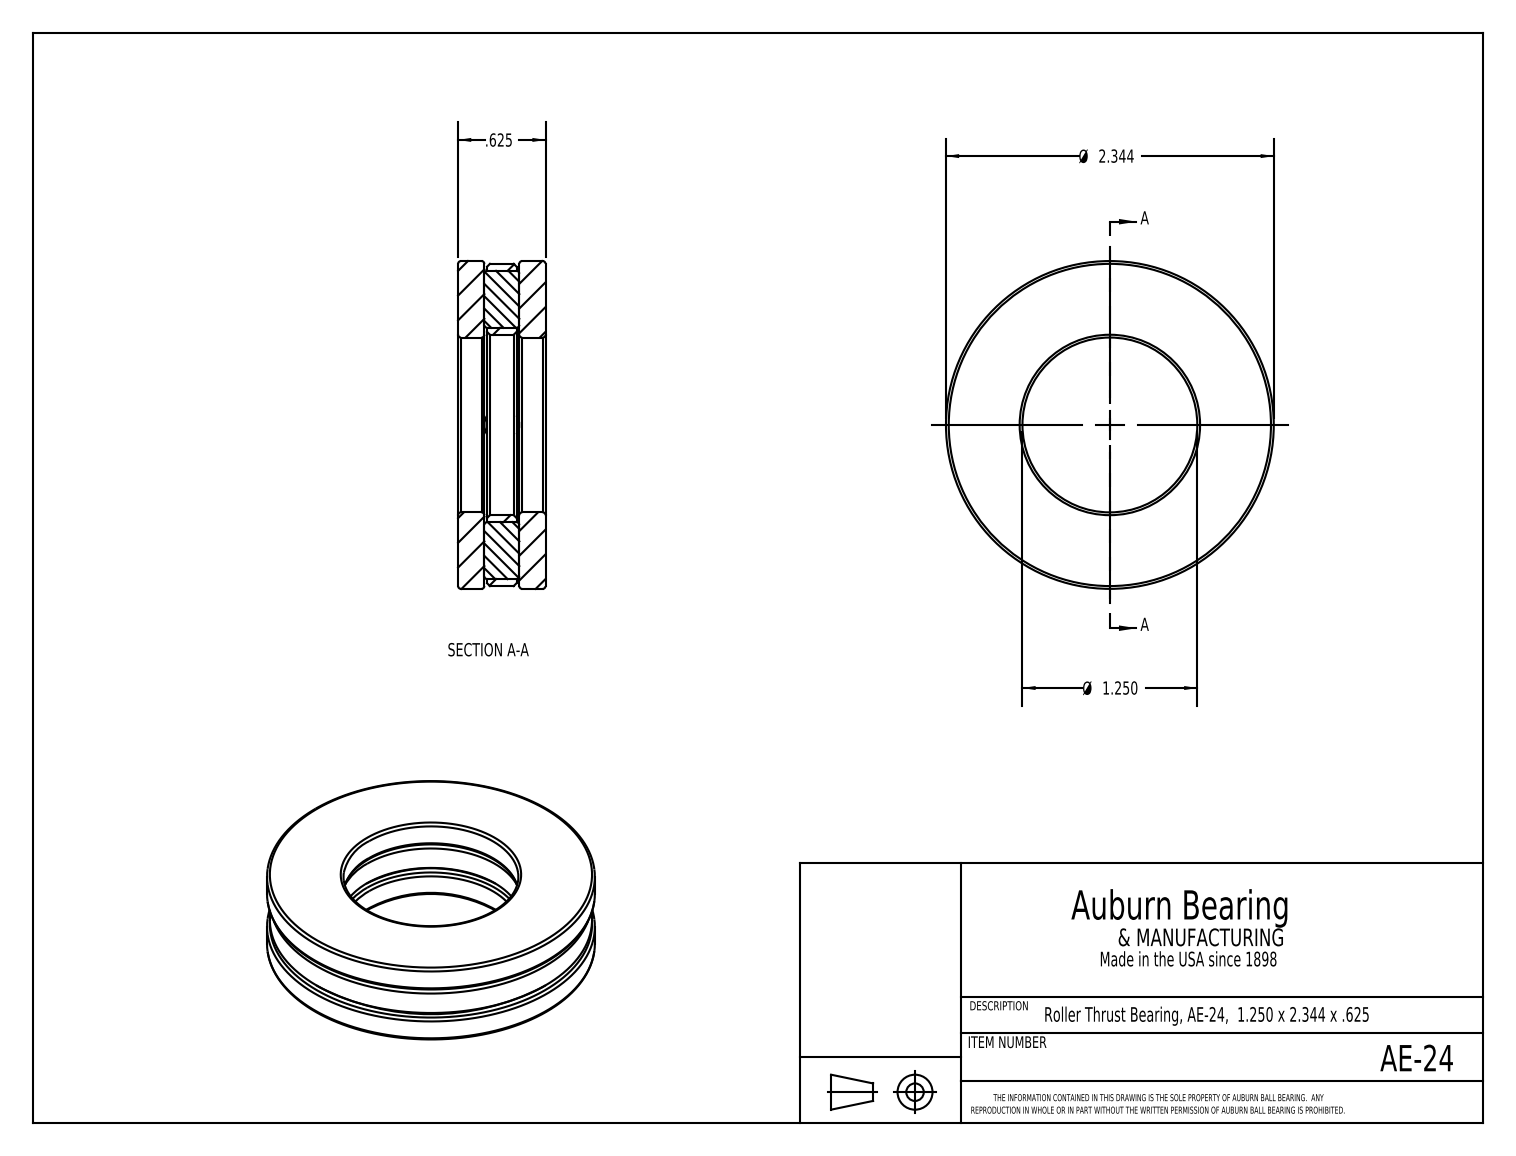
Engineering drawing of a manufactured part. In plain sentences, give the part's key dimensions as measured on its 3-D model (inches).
The part is named "AE-24". Its 3-D file was written by "SolidWorks 2017 (CONFIG_CONTROL_DESIGN)". It is 7 solids with 60 faces: 30 planar, 10 cylindrical and 20 other. Overall it measures 2.344 by 2.344 by 0.625 inches. Its volume is 1.744 cubic inches and its surface area 25.93 square inches. Round holes: 1 of diameter 1.25, 1 of diameter 1.29. Round bosses or shafts: 2 of diameter 0.25, 1 of diameter 2.344, 1 of diameter 2.304. The main face-to-face distances are 0.207, 0.418, 0.25, 0.187, 0.437, 0.625, 0.438, 0.188, 0.23, 0.02.
